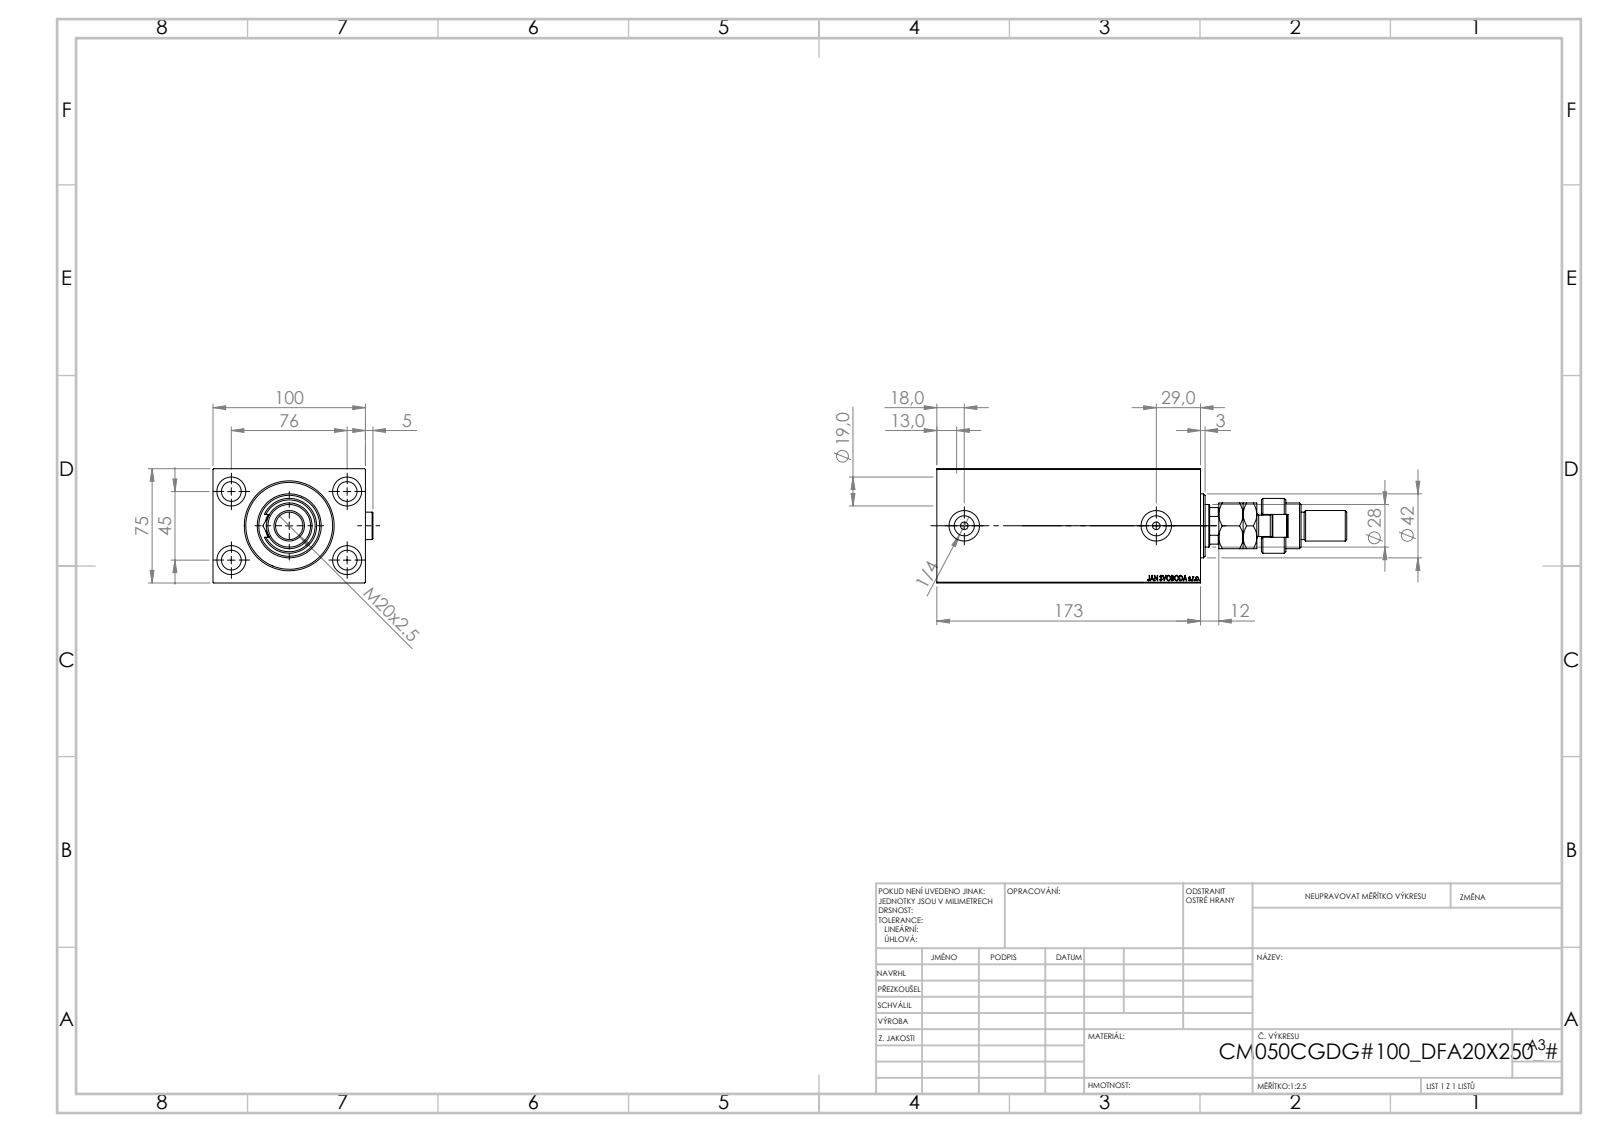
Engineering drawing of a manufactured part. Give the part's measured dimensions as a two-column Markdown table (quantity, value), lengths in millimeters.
| quantity | value |
| --- | --- |
| part name | Zatka_OIL_PORT; V450CM_C_VCP; V450CM_VC_B; MFA (+2 more) |
| STEP written by | SolidWorks 2019 (CONFIG_CONTROL_DESIGN) |
| units | millimeters |
| bodies | 7 solids, 1004 faces (471 planar, 91 cylindrical, 442 other) |
| overall size | 269 × 104.9 × 75 |
| volume | 1 100 000 mm³ |
| surface area | 178 568 mm² |
| round holes (diameter × count) | 13 × 4, 19 × 4, 5 × 2, 13.16 × 2, 20 × 2, 18.5 × 1, 28 × 1, 31.5 × 1, 50 × 1, 52 × 1, 57 × 1 |
| round bosses / shafts (diameter × count) | 18 × 3, 42 × 1, 36 × 1, 30 × 1, 22 × 1, 20 × 1, 14 × 1 |
| partial cylindrical surfaces (radius × count) | 7.5 × 1, 12 × 1, 13.5 × 1 |
| main face-to-face distances | 75, 100, 173, 159, 14, 12, 147, 30, 161, 47 |
| hole center spacings | 44.16, 45, 76, 88.32, 126 |
